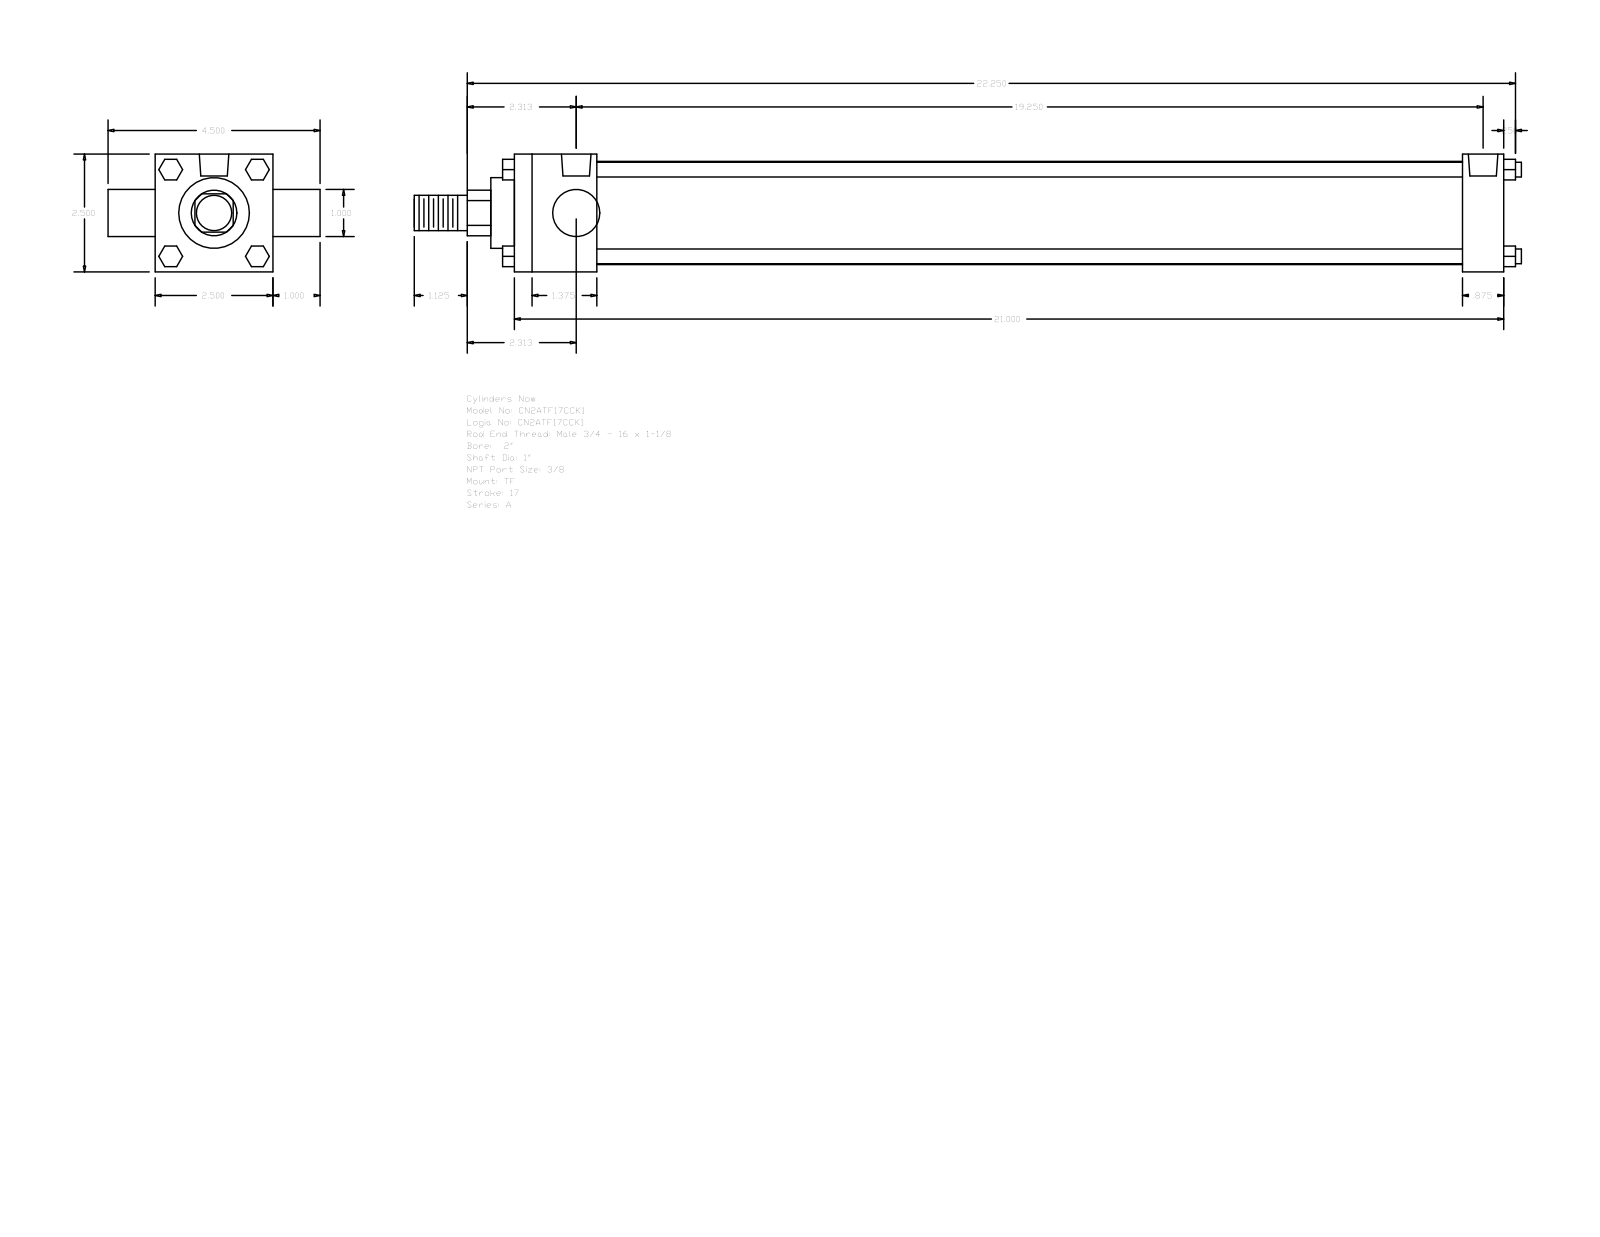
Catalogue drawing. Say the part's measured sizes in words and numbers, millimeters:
The part is named "A_TF__0200_1". Its 3-D file was written by "GSSL Pune (CONFIG_CONTROL_DESIGN)". It is 0 solids with 120 faces: 92 planar, 28 cylindrical and 0 other. Overall it measures 596.9 by 114.3 by 63.5 millimeters. Round holes: 3 of diameter 5.56, 2 of diameter 15.93. Round bosses or shafts: 4 of diameter 7.94, 2 of diameter 25.4, 1 of diameter 55.63, 1 of diameter 38.1, 1 of diameter 19.05. Partial cylindrical surfaces (rounded edges, fillets, slot ends): 1 of radius 12.29. The main face-to-face distances are 63.5, 533.4, 44.45, 511.18, 466.73, 488.95, 22.22, 25.4, 88.9, 546.1. The hole center spacings are 1.59, 3.98, 483.38, 484.97, 487.36, 488.95.
